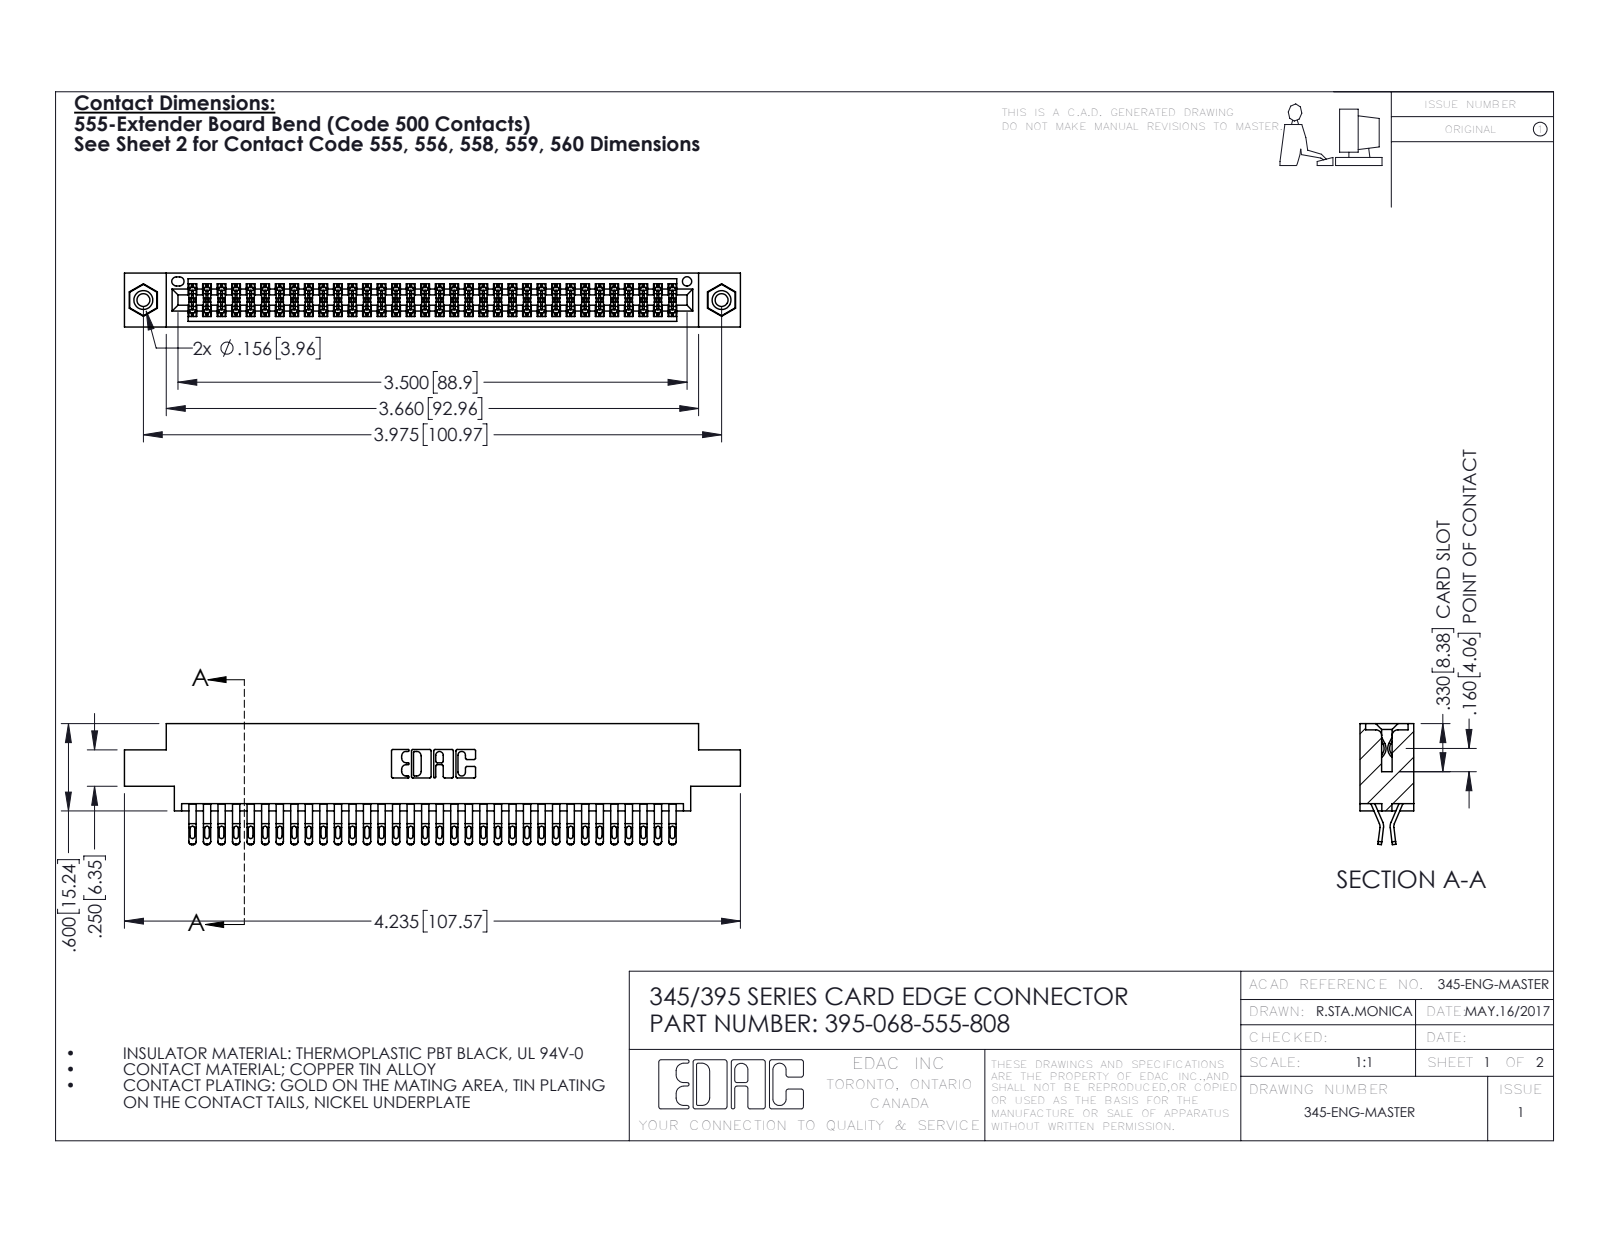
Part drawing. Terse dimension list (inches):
name: 345-292-001_555 Tail; 395-068-555-808; 345 Part_0.170 Offset - 0.156 Dia-TI; 345-250-001_345-250-003-102
written by: SolidWorks 2016 (CONFIG_CONTROL_DESIGN)
unit: in
bodies: 71 solids, 3998 faces (2224 planar, 1758 cylindrical, 16 other)
size: 4.235 × 0.832 × 0.37
volume: 0.638 in³; area: 25.01 in²
holes: 2× ⌀0.089, 2× ⌀0.125, 2× ⌀0.156, 1× ⌀0.064
bosses: 2× ⌀0.155
rounds: 170× R0.016, 136× R0.02, 102× R0.006, 22× R0.01, 6× R0.007, 6× R0.031, 3× R0.026, 2× R0.01
face distances: 0.072, 0.298, 0.37, 0.025, 0.2, 0.098, 0.272, 0.225, 0.175, 0.149
hole spacings: 0.27, 3.74, 3.975
